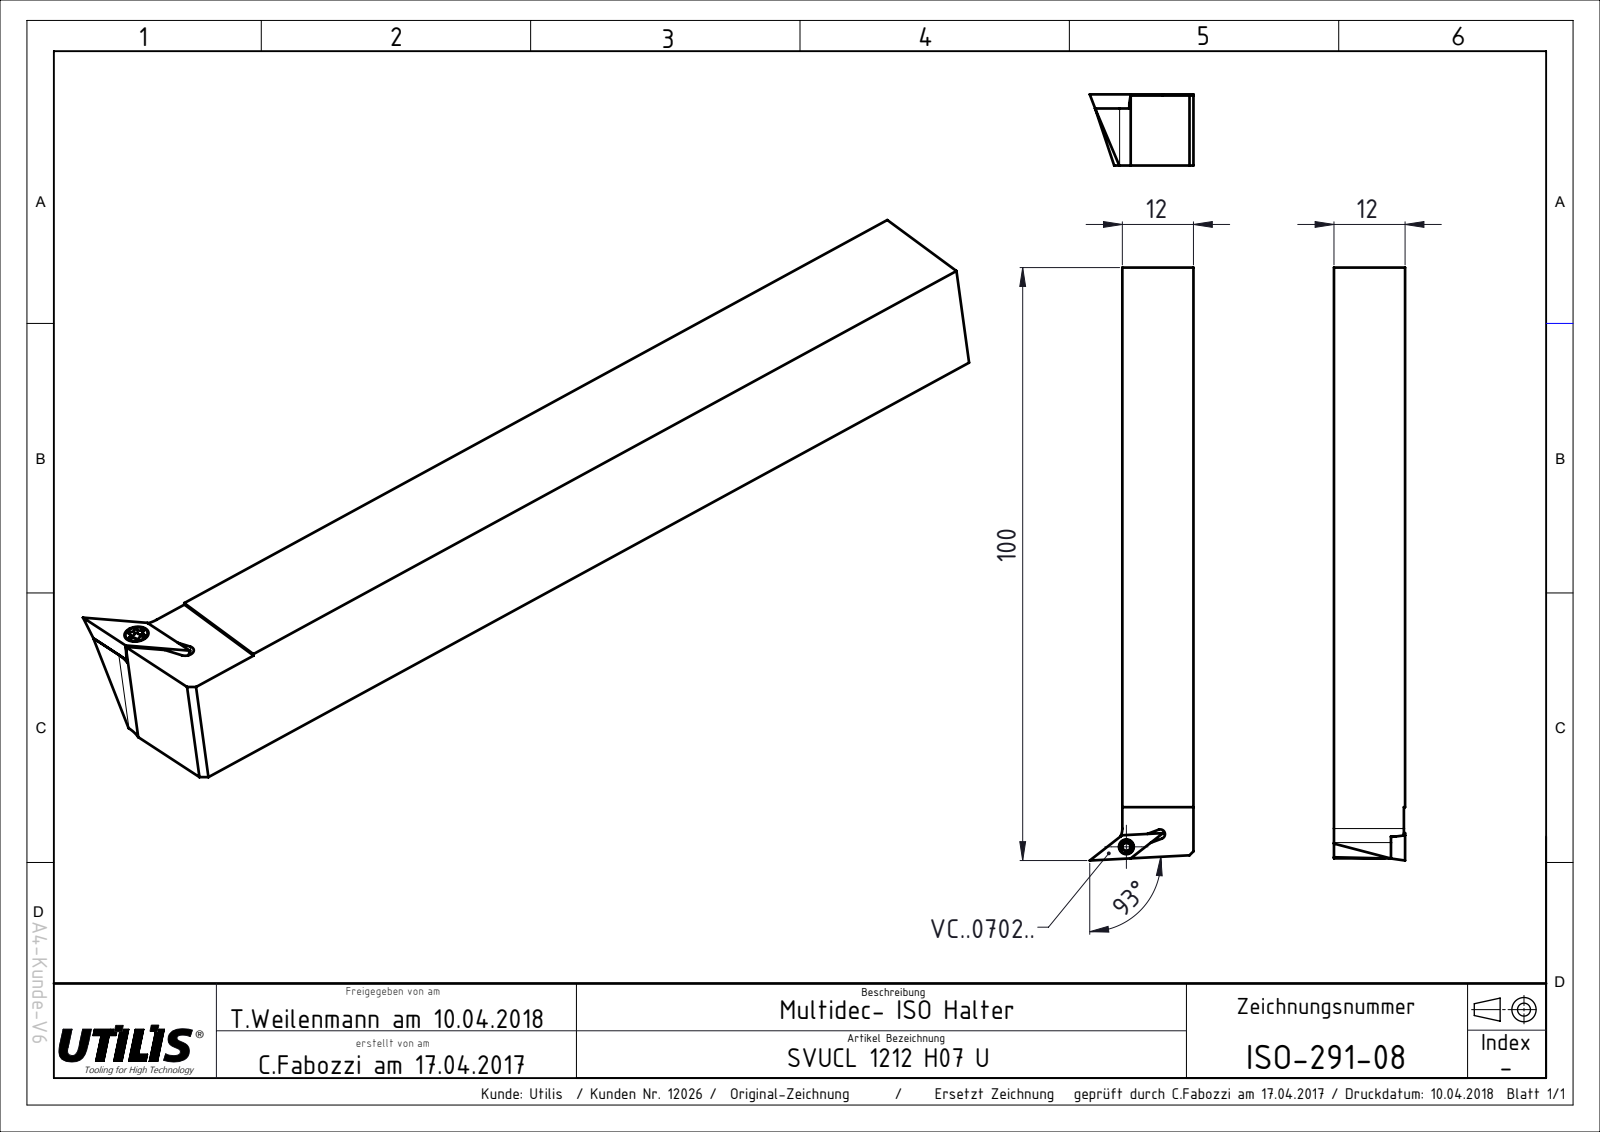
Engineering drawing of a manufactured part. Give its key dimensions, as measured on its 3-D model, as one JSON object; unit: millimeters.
{"part_name": "ISO-291-08", "step_written_by": "SolidWorks 2017 (AUTOMOTIVE_DESIGN)", "units": "millimeters", "bodies": {"solids": 1, "faces": 29, "planar": 26, "cylindrical": 3, "other": 0}, "overall_size": [100, 17.5, 12], "volume_mm3": 14368, "surface_area_mm2": 5168, "partial_cylinders_radius": [[0.8, 1], [3, 1], [6.1, 1]], "face_to_face_distances": [12, 11.8, 3.49, 1.6, 9.62, 2.18, 2.38, 3.77, 91]}
